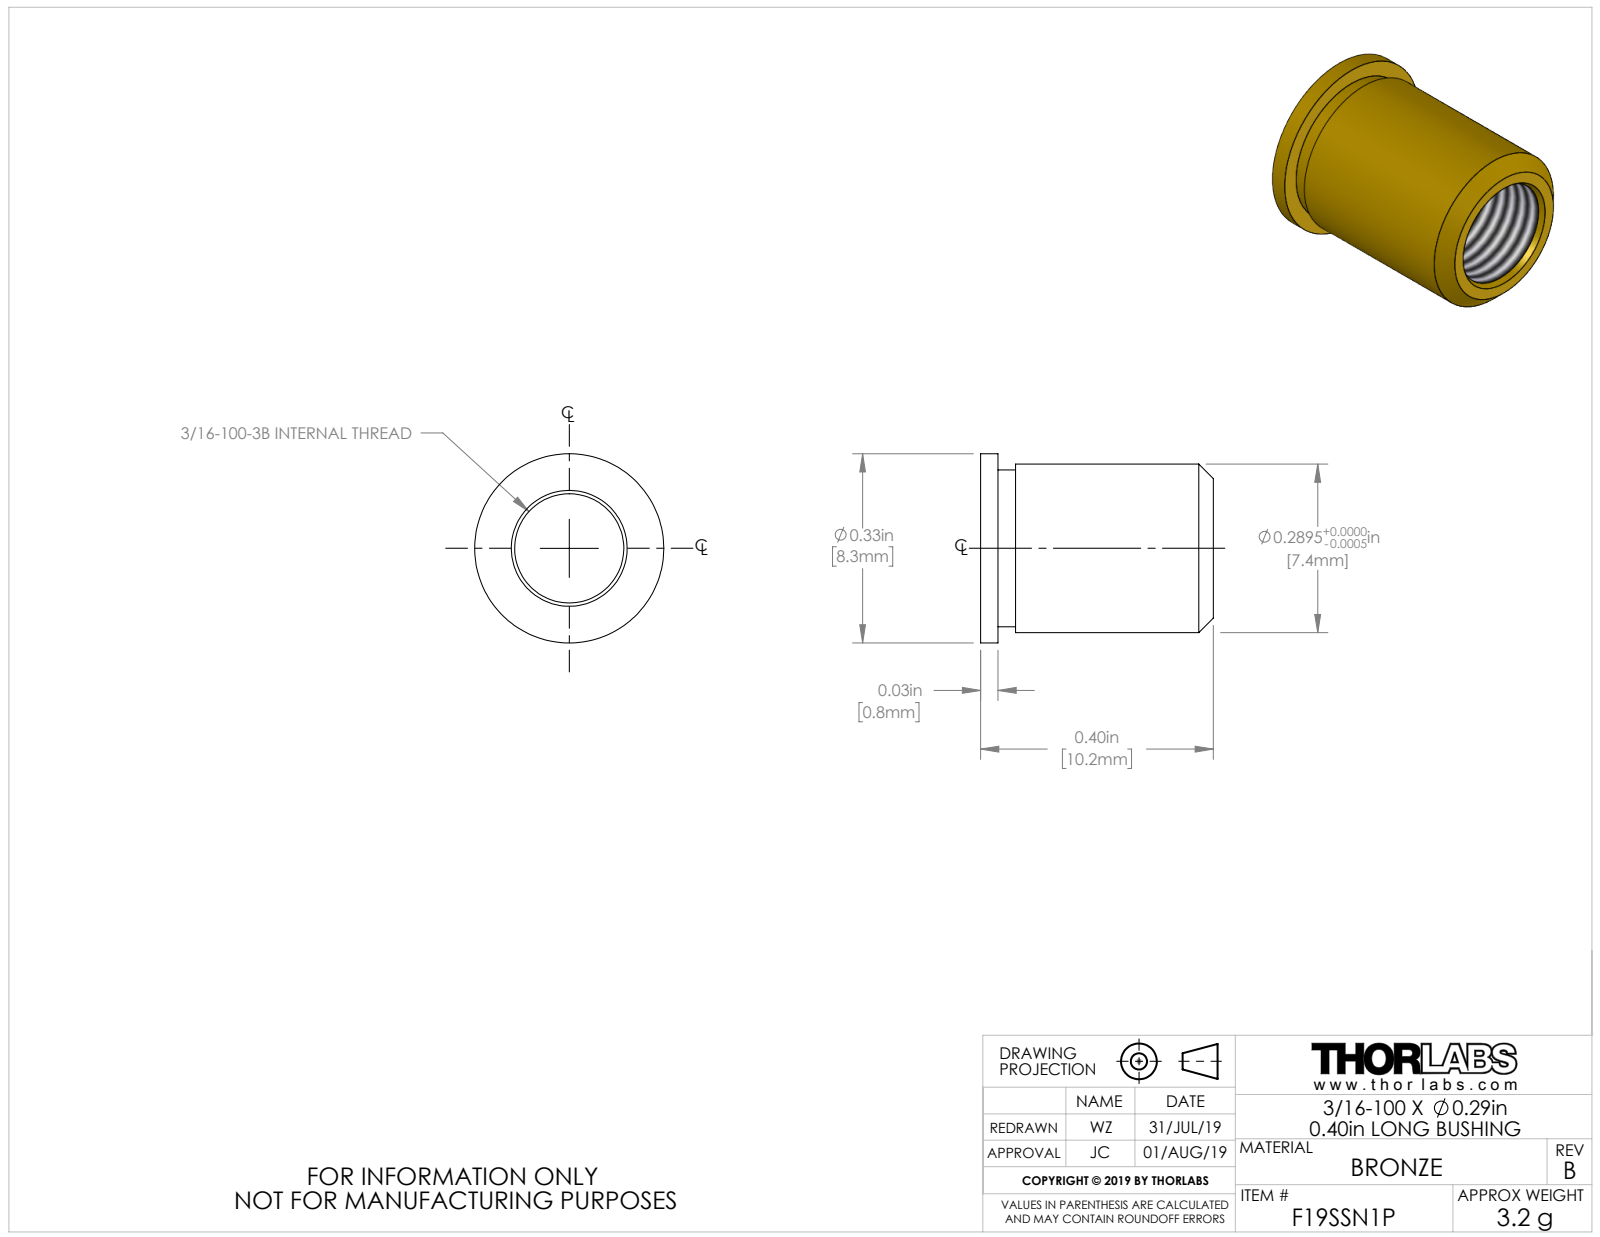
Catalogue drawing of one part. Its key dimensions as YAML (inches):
part_name: "18988-E0W"
step_written_by: "SolidWorks 2007 (AUTOMOTIVE_DESIGN)"
units: inches
bodies: {solids: 1, faces: 18, planar: 4, cylindrical: 8, other: 6}
overall_size: [0.4, 0.325, 0.325]
volume: 0.015
surface_area: 0.71
round_holes:
  - {diameter: 0.187, count: 1}
round_bosses_or_shafts:
  - {diameter: 0.325, count: 1}
  - {diameter: 0.289, count: 1}
  - {diameter: 0.27, count: 1}
face_to_face_distances: [0.03, 0.4, 0.37, 0.06, 0.34]
